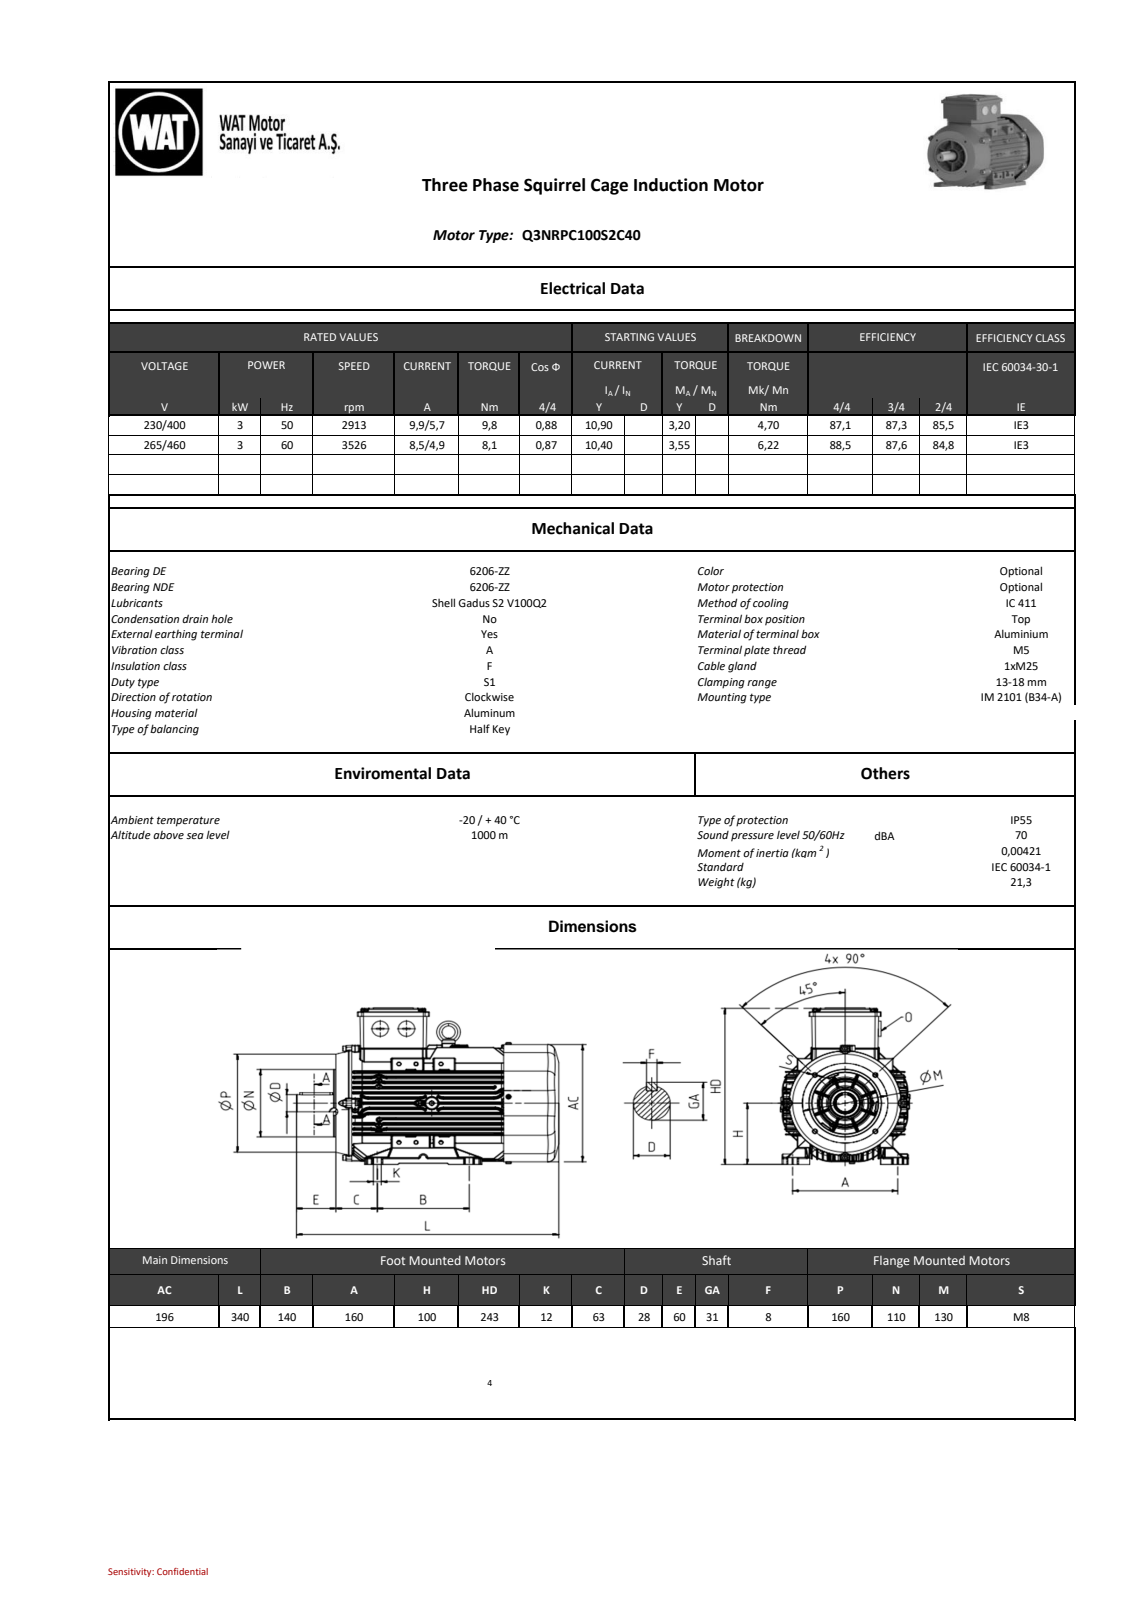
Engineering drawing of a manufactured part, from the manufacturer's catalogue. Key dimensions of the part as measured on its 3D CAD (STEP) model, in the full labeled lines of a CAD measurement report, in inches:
Part name (STEP PRODUCT): C90127E0127Fj9a8
STEP written by: SIEMENS PLM Software NX 11.0 (AUTOMOTIVE_DESIGN)
Units: inches
Bodies: 0 solids, 13577 faces (2820 planar, 4228 cylindrical, 6529 other)
Overall size (bounding box): 13.386 × 9.075 × 7.874
Round holes (diameter × count): ⌀0.197 ×6, ⌀0.256 ×6, ⌀0.268 ×4, ⌀0.079 ×2, ⌀0.098 ×2, ⌀0.118 ×2, ⌀0.472 ×2, ⌀0.984 ×2, ⌀0.157 ×1, ⌀0.335 ×1, ⌀0.413 ×1, ⌀1.126 ×1
Round bosses / shafts (diameter × count): ⌀0.315 ×7, ⌀0.157 ×7, ⌀0.465 ×6, ⌀0.394 ×6, ⌀0.236 ×6, ⌀1.378 ×2, ⌀1.094 ×2, ⌀0.994 ×2
Partial cylindrical surfaces — rounded edges, fillets, slot ends (radius × count): R0.02 ×1176, R0.03 ×576, R0.031 ×533, R0.039 ×296, R0.01 ×144, R0.157 ×102, R0.059 ×94, R0.079 ×83
Main face-to-face distances: 0.031, 0.079, 1.614, 9.409, 0.551, 1.583, 0.208, 11.024, 10.992, 1.102
Hole centre spacings: 3.622, 1.427, 1.535, 2.559, 2.561, 3.619, 3.733, 3.785
